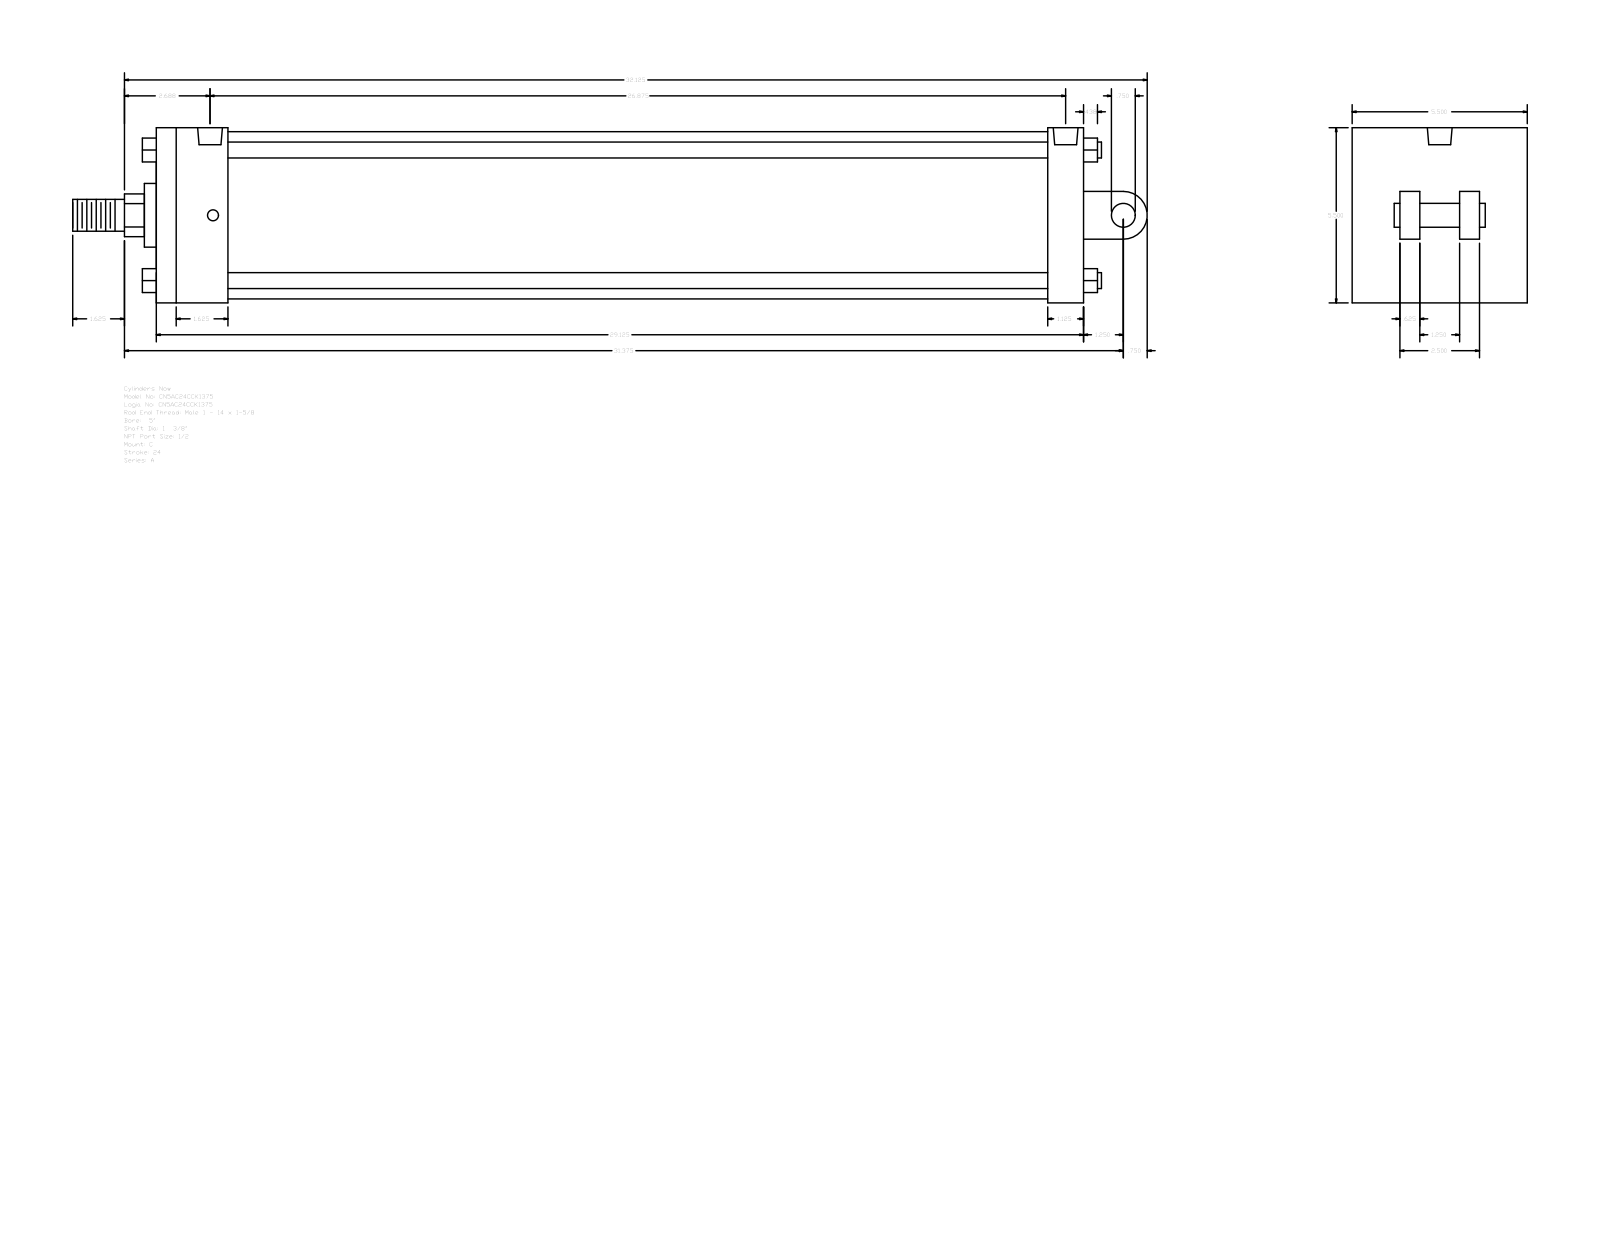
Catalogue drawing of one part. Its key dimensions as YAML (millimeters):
part_name: "A_C__0500_1.375"
step_written_by: "GSSL Pune (CONFIG_CONTROL_DESIGN)"
units: millimeters
bodies: {solids: 0, faces: 135, planar: 102, cylindrical: 33, other: 0}
overall_size: [857.25, 139.7, 139.7]
round_holes:
  - {diameter: 8.73, count: 4}
  - {diameter: 19.77, count: 2}
round_bosses_or_shafts:
  - {diameter: 12.7, count: 4}
  - {diameter: 133.35, count: 1}
  - {diameter: 50.8, count: 1}
  - {diameter: 34.92, count: 1}
  - {diameter: 25.4, count: 1}
  - {diameter: 19.05, count: 1}
partial_cylinders:
  - {radius: 17.06, count: 1}
  - {radius: 19.05, count: 1}
face_to_face_distances: [139.7, 739.77, 57.15, 711.2, 654.05, 682.62, 28.57, 38.1, 53.97, 85.73]
hole_center_spacings: [2.39, 677.85, 680.24, 682.63]
